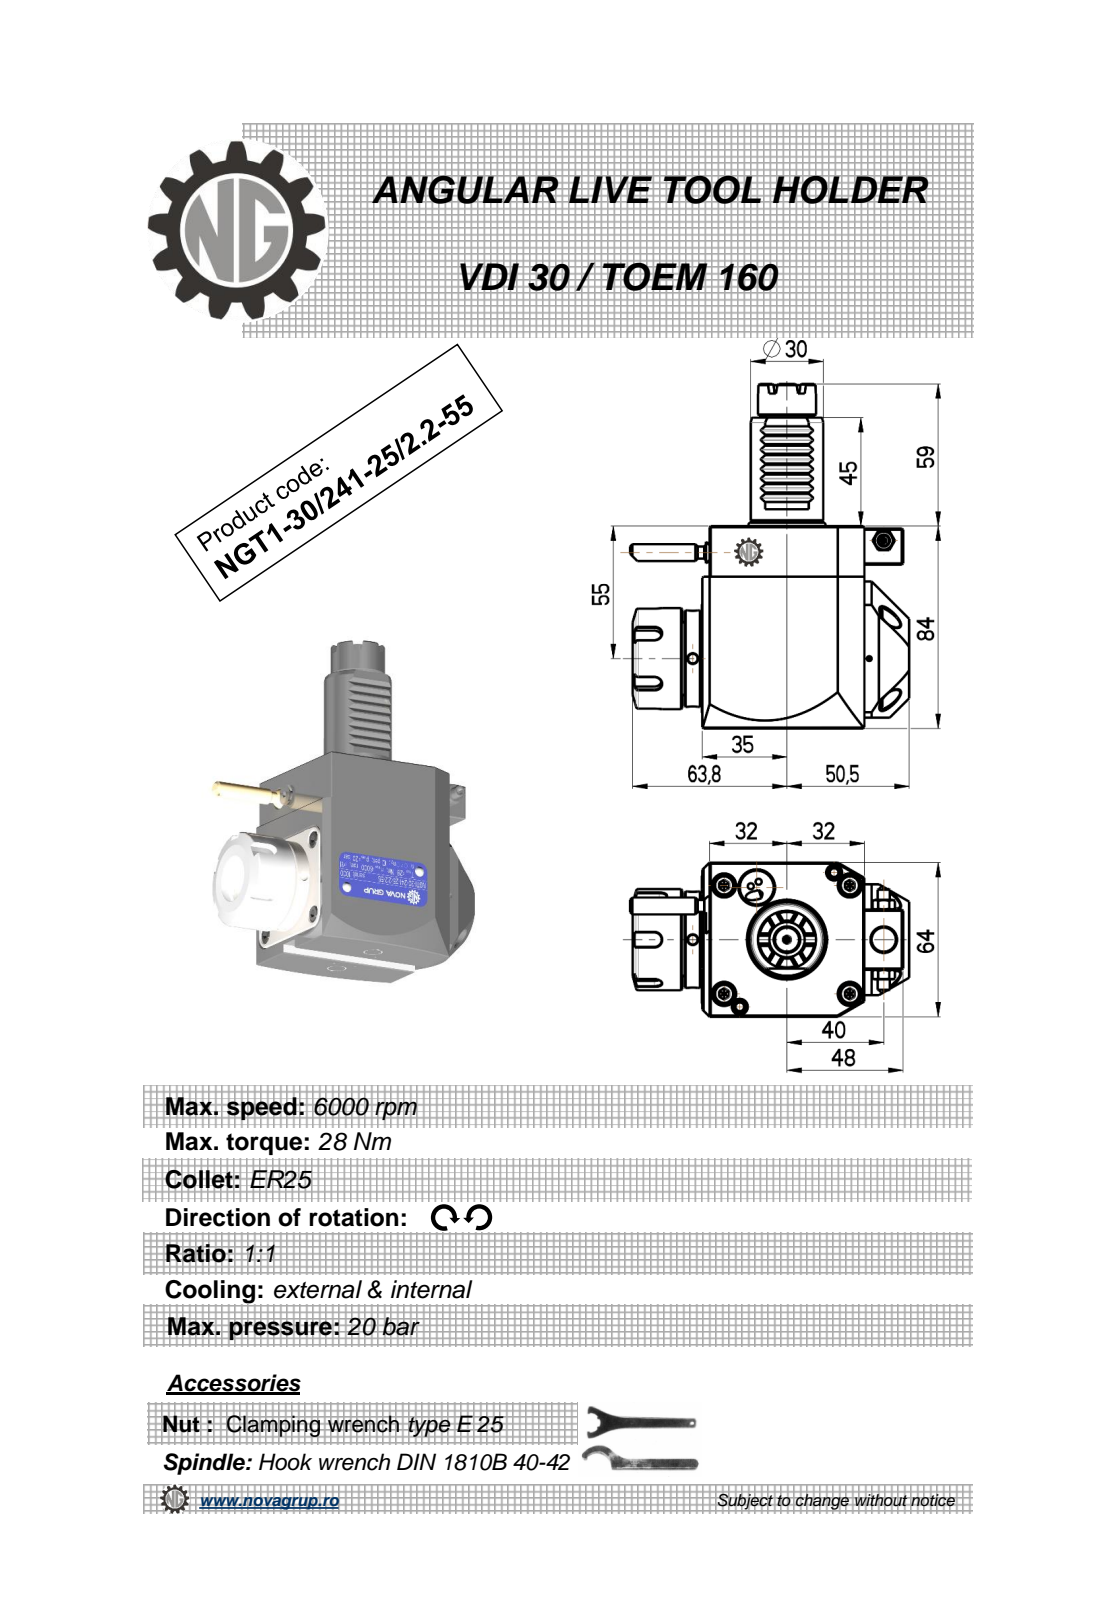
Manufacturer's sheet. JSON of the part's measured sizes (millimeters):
{"part_name": "NGT1_30_241_25_2_2_55", "step_written_by": "PRO/ENGINEER BY PARAMETRIC TECHNOLOGY CORPORATION, 2010280 (CONFIG_CONTROL_DESIGN)", "units": "millimeters", "bodies": {"solids": 1, "faces": 449, "planar": 208, "cylindrical": 90, "other": 151}, "overall_size": [143, 115.38, 65.6], "volume_mm3": 455682, "surface_area_mm2": 46739, "round_holes": [[4, 2], [2.5, 1], [3, 1], [4.2, 1], [9.5, 1], [10, 1], [20.3, 1]], "round_bosses_or_shafts": [[8.96, 2], [5, 2], [42, 1], [40, 1], [33, 1], [30, 1], [24, 1], [17.7, 1]], "partial_cylinders_radius": [[0.26, 12], [0.3, 8], [3, 5], [160, 2], [7.6, 1], [32, 1]], "face_to_face_distances": [64, 84, 67.2, 67, 3.2, 3, 80, 0.5, 85.7, 85.5], "hole_center_spacings": [14.22, 46.17, 46.5, 78.95, 92.92]}
